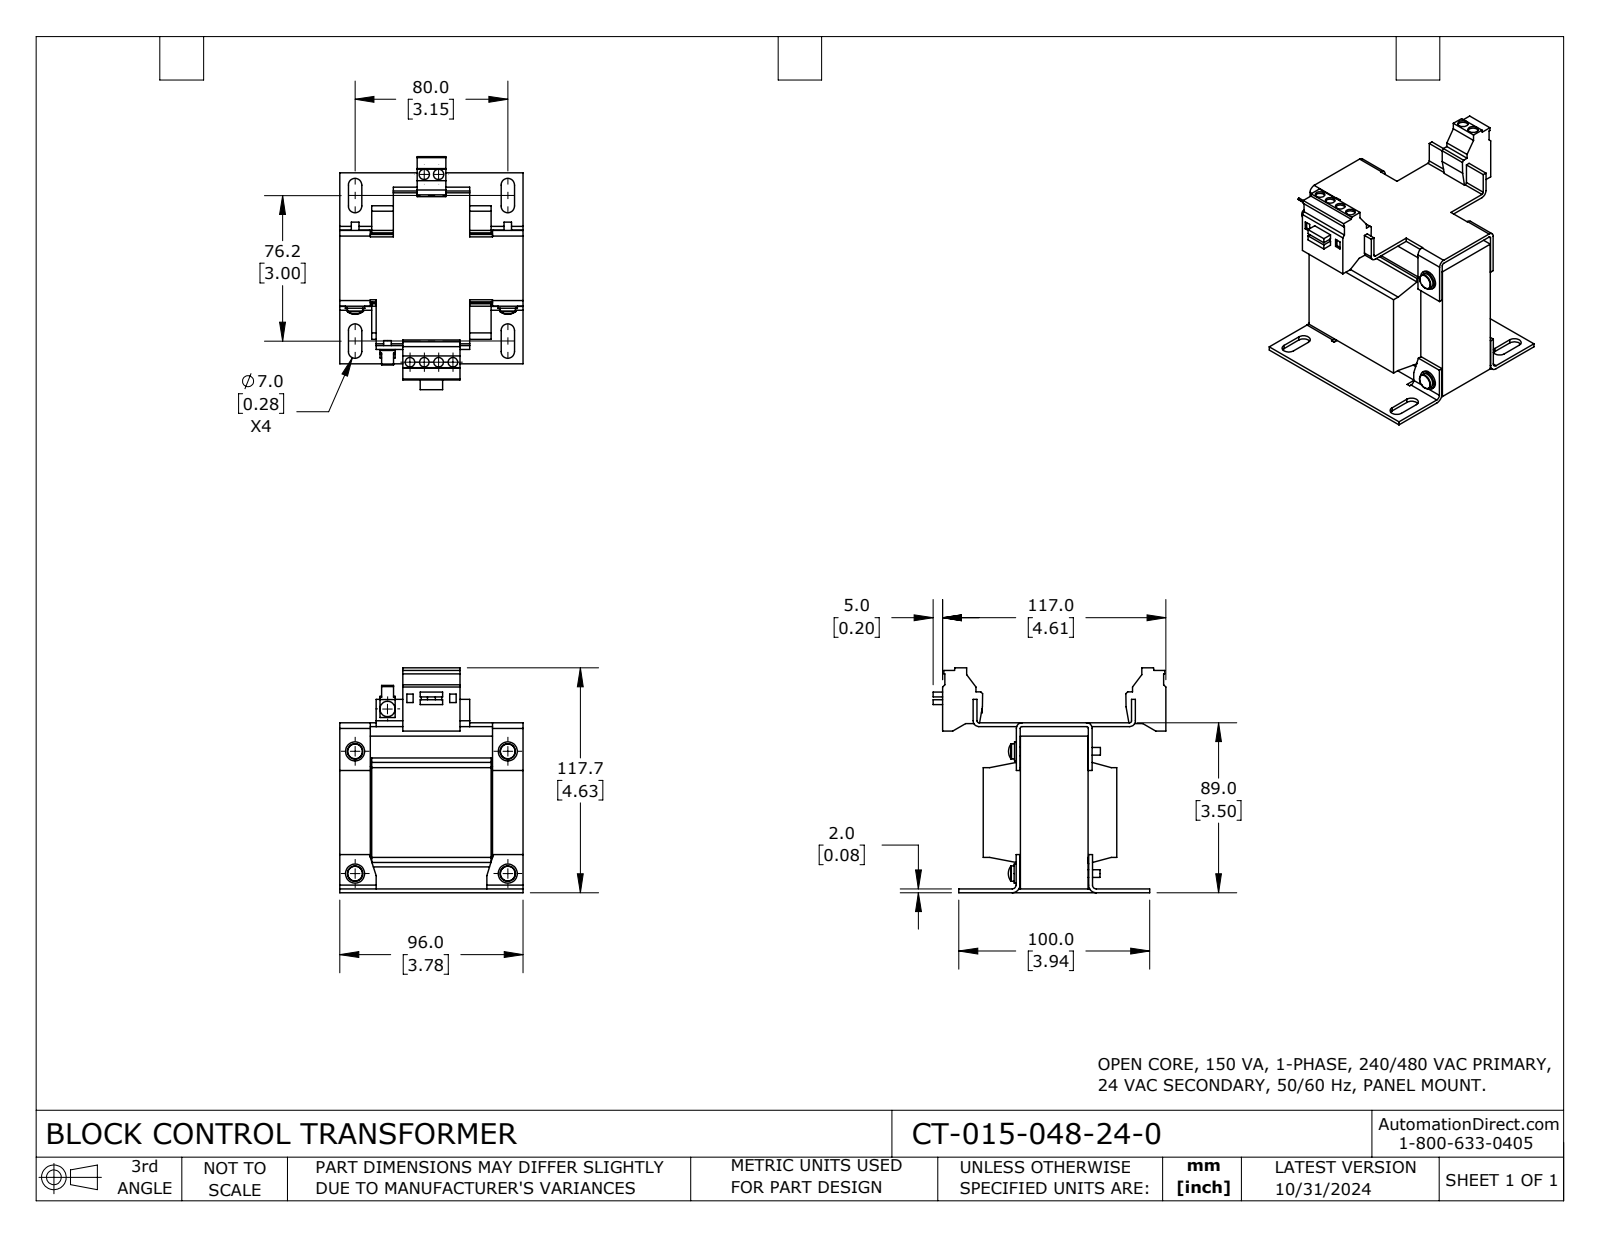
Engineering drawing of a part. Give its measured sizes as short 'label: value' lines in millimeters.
name: CT-015-048-24-0
written by: SolidWorks 2023 (CONFIG_CONTROL_DESIGN)
unit: mm
bodies: 1 solid, 341 faces (241 planar, 88 cylindrical, 12 other)
size: 122 × 117.7 × 96
volume: 435 600 mm³; area: 87 550 mm²
holes: 4× ⌀5, 2× ⌀5.4
bosses: 5× ⌀8, 5× ⌀4, 4× ⌀10, 4× ⌀4.5
rounds: 8× R3.5, 4× R1, 4× R3, 2× R2, 2× R4
face distances: 2, 87, 80, 16.7, 79.3, 16, 85, 89, 35.5, 64
hole spacings: 7.5, 98.7, 15, 98.4, 99.5, 22.5
